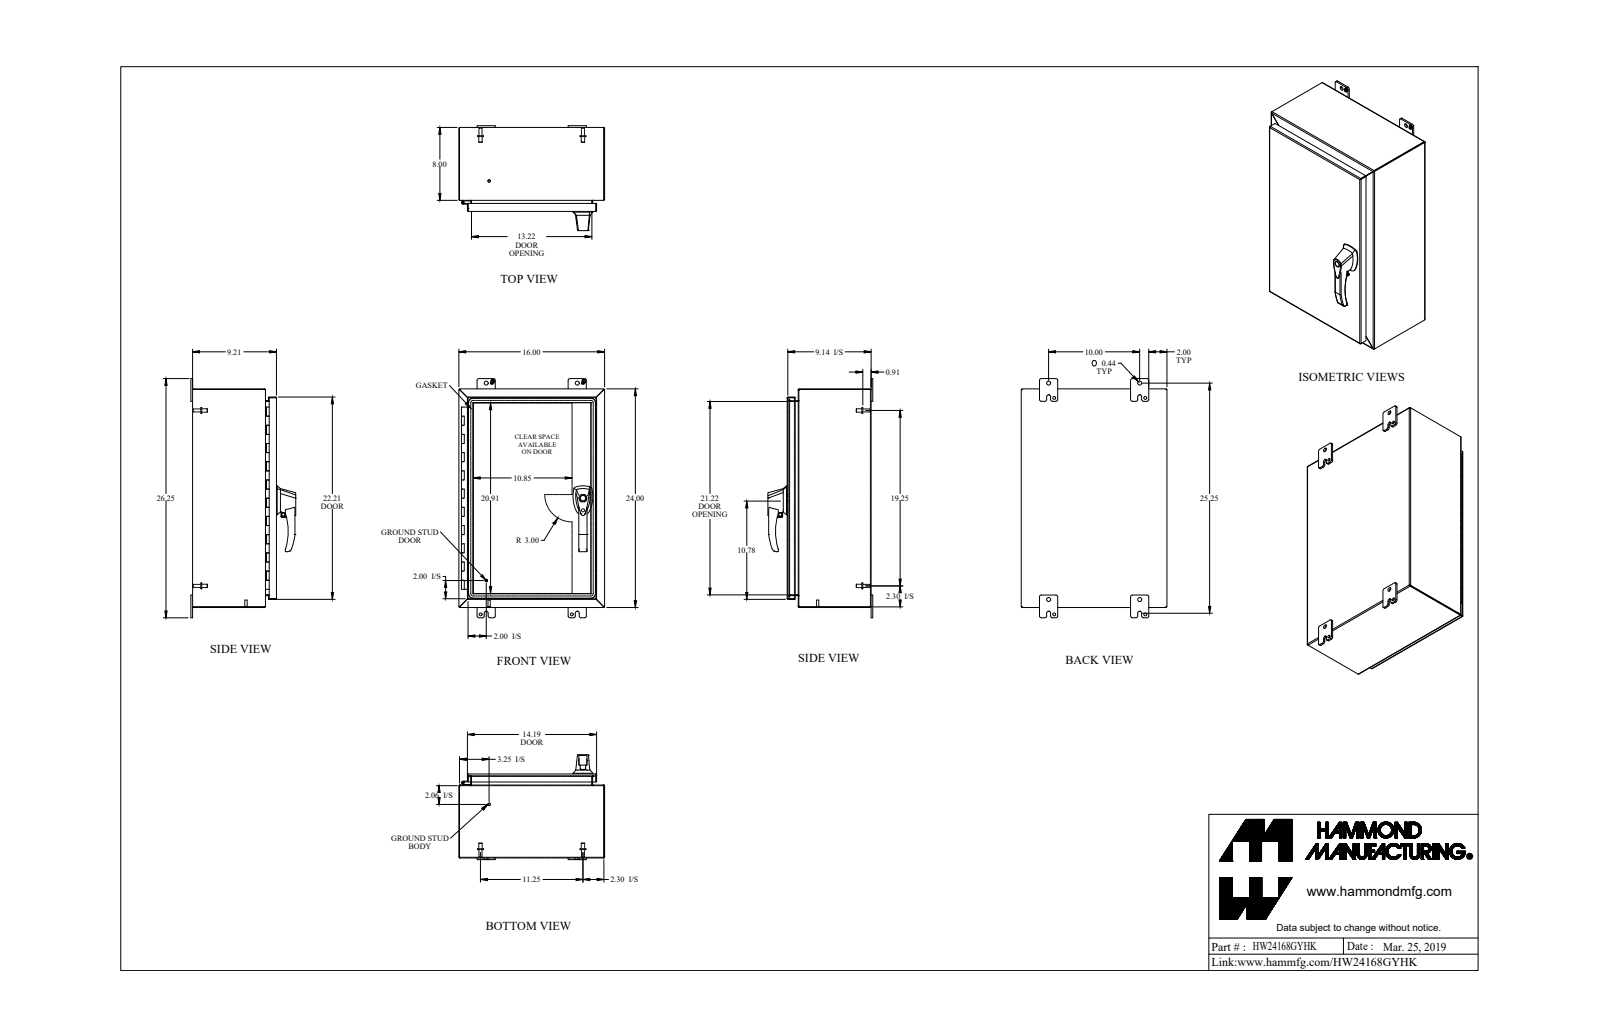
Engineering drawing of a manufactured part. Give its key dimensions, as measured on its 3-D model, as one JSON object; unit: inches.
{"part_name": "HW24168GYHK", "step_written_by": "SolidWorks 2018 (AUTOMOTIVE_DESIGN)", "units": "inches", "bodies": {"solids": 43, "faces": 1384, "planar": 686, "cylindrical": 553, "other": 145}, "overall_size": [26.25, 16, 11.512], "volume_in3": 147, "surface_area_in2": 3672, "round_holes": [[0.176, 6], [0.313, 4], [0.25, 3], [0.265, 3], [0.413, 3], [0.196, 2], [0.256, 2], [0.394, 2], [0.437, 2], [0.187, 1], [0.233, 1], [0.334, 1]], "round_bosses_or_shafts": [[0.375, 9], [0.25, 7], [0.156, 6], [0.65, 4], [0.33, 4], [1, 3], [0.63, 2], [0.51, 2]], "partial_cylinders_radius": [[0.25, 27], [0.188, 24], [0.036, 20], [0.108, 20], [0.06, 12], [0.125, 9], [0.045, 8], [0.218, 8]], "face_to_face_distances": [0.072, 0.072, 15.928, 9.138, 9.066, 9.21, 9.138, 23.928, 7.928, 15.856], "hole_center_spacings": [8.118, 8.119, 16.237, 1.111, 8.119, 10, 1.005, 1.005]}
